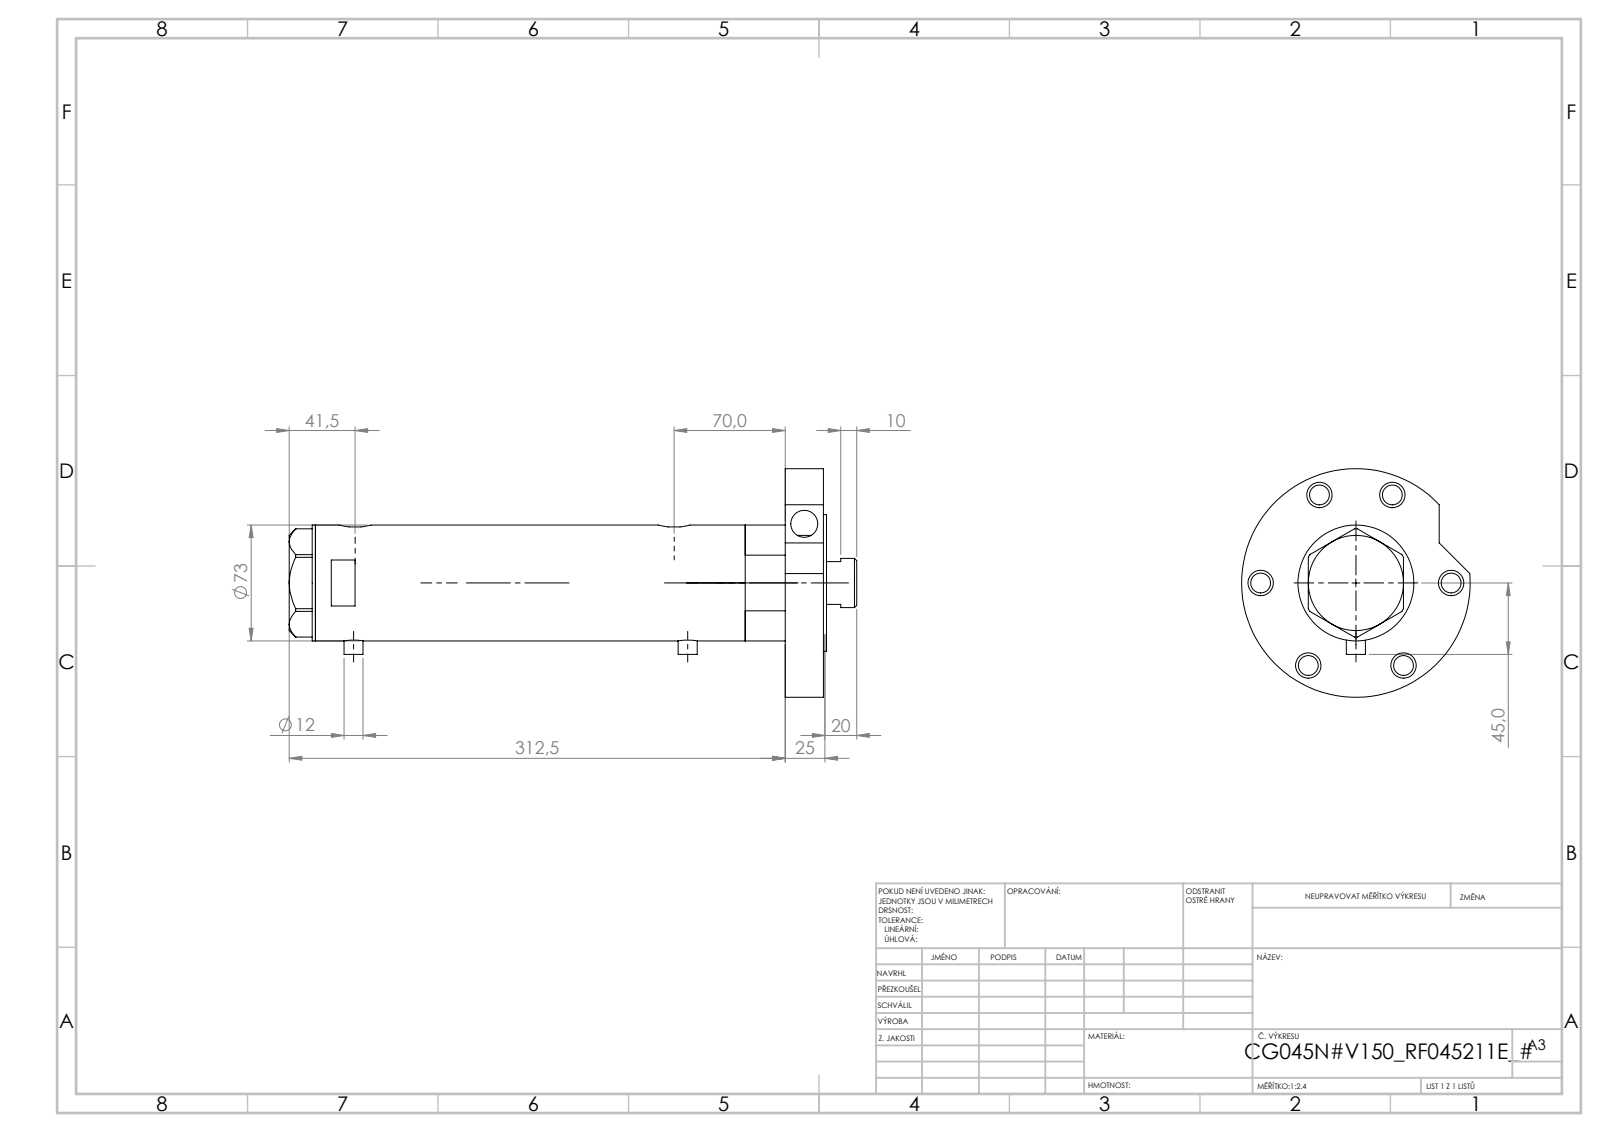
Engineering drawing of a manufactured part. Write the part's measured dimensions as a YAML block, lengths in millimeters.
part_name: "V270CG_BACK; V270CG_MIDDLE; V270CG_VC; V270CG_RF211E (+1 more)"
step_written_by: "SolidWorks 2019 (CONFIG_CONTROL_DESIGN)"
units: millimeters
bodies: {solids: 5, faces: 164, planar: 60, cylindrical: 84, other: 20}
overall_size: [357.5, 144, 144]
volume: 1521000
surface_area: 251146
round_holes:
  - {diameter: 12.5, count: 8}
  - {diameter: 16, count: 6}
  - {diameter: 13.16, count: 2}
  - {diameter: 10.5, count: 1}
  - {diameter: 17, count: 1}
  - {diameter: 32, count: 1}
  - {diameter: 33.5, count: 1}
  - {diameter: 45, count: 1}
  - {diameter: 48, count: 1}
  - {diameter: 60, count: 1}
  - {diameter: 64, count: 1}
round_bosses_or_shafts:
  - {diameter: 12, count: 2}
  - {diameter: 144, count: 1}
  - {diameter: 86, count: 1}
  - {diameter: 73, count: 1}
  - {diameter: 58, count: 1}
  - {diameter: 31, count: 1}
partial_cylinders:
  - {radius: 10, count: 2}
face_to_face_distances: [24, 296, 26, 2, 320, 322, 226, 70, 94, 1]
hole_center_spacings: [60, 66.67, 99.77, 103.92, 107.62, 119.74, 1, 8.5]
